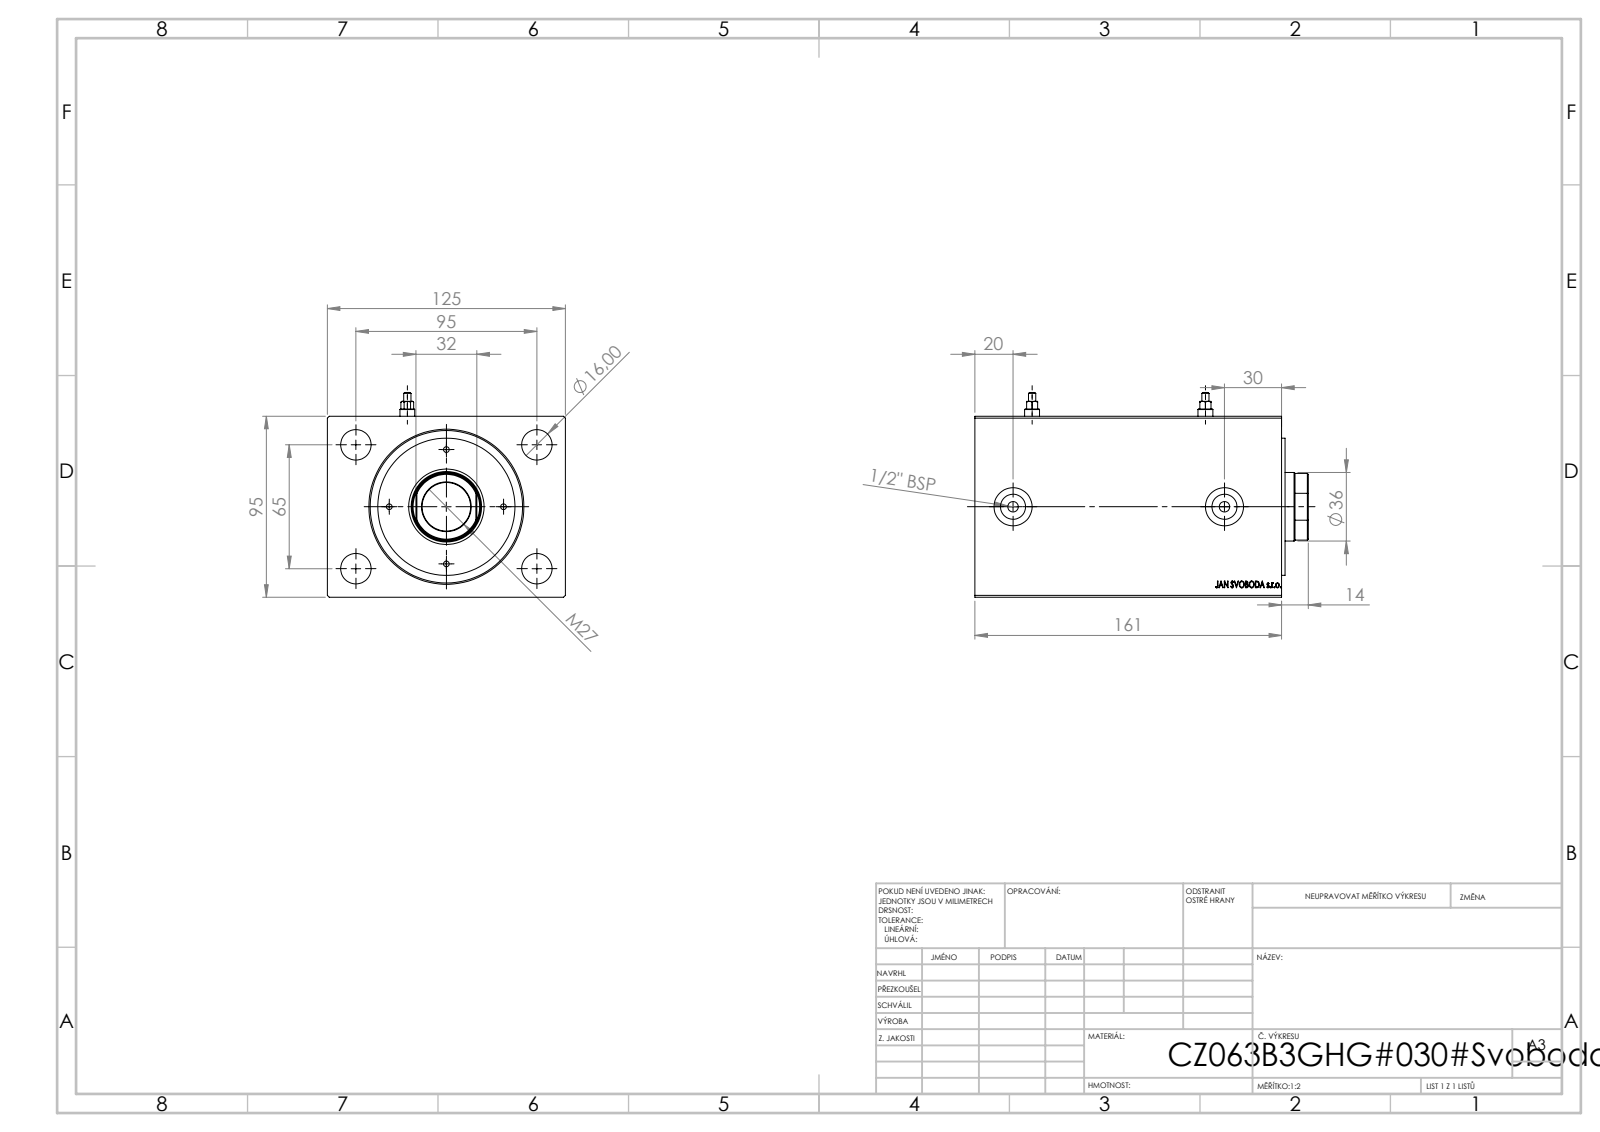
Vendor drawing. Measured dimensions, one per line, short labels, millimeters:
name: V500CZ; Zatka_Cushioning3; V500CZ_B_VC
written by: SolidWorks 2019 (CONFIG_CONTROL_DESIGN)
unit: mm
bodies: 5 solids, 934 faces (424 planar, 74 cylindrical, 436 other)
size: 175 × 125 × 107.5
volume: 1 790 000 mm³; area: 183 258 mm²
holes: 4× ⌀3, 4× ⌀16, 2× ⌀1.8, 2× ⌀5.5, 2× ⌀8, 2× ⌀13.16, 2× ⌀20, 1× ⌀25.5, 1× ⌀36, 1× ⌀37, 1× ⌀63, 1× ⌀80
bosses: 2× ⌀7.8, 2× ⌀3.8, 1× ⌀72
rounds: 1× R17.5
face distances: 95, 125, 161, 140.2, 20.8, 14, 1.8, 12.2, 128, 148.8
hole spacings: 30, 36.91, 42.43, 47.57, 57.55, 78.5, 84.04, 60
